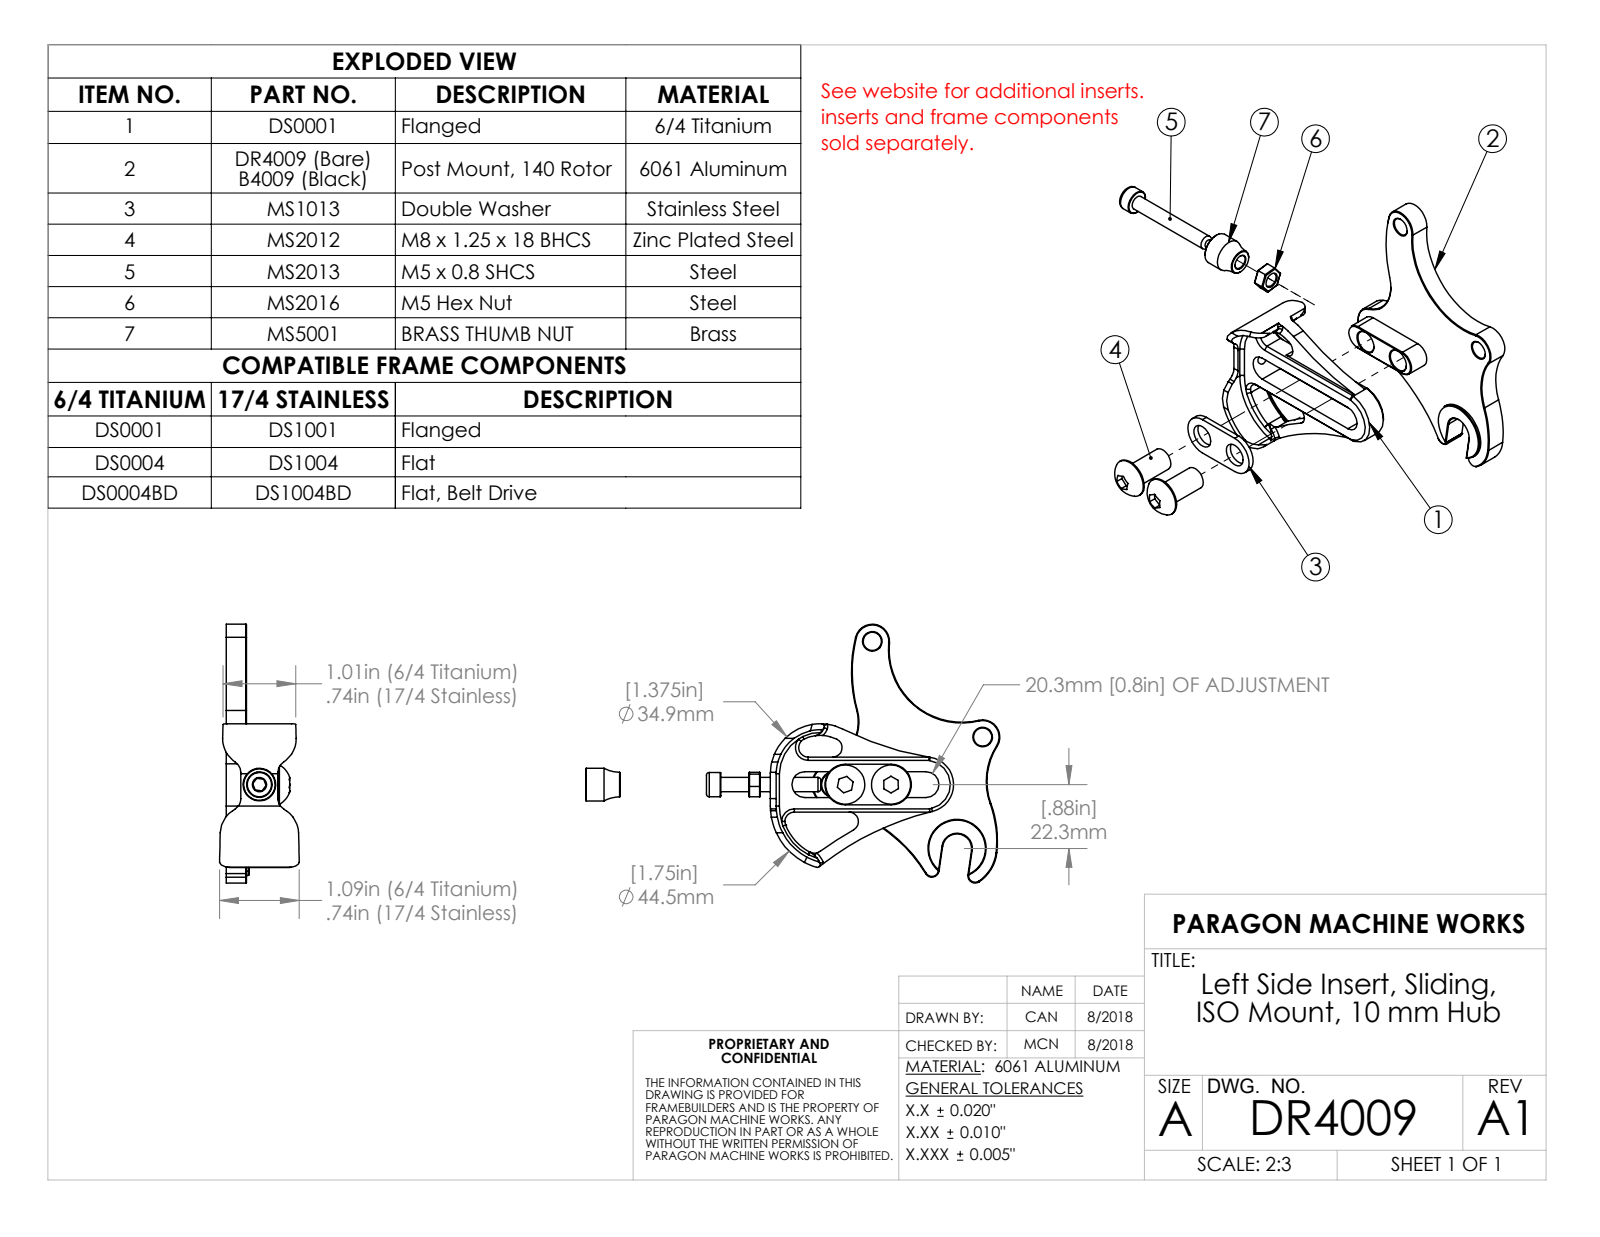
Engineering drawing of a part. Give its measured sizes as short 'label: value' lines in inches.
name: DR4009
written by: SolidWorks 2023 (AUTOMOTIVE_DESIGN)
unit: in
bodies: 1 solid, 73 faces (8 planar, 35 cylindrical, 30 other)
size: 3.53 × 2.37 × 0.585
volume: 1.281 in³; area: 14.18 in²
holes: 2× ⌀0.25, 2× ⌀0.312
bosses: 1× ⌀0.8
rounds: 4× R0.01, 2× R0.1, 2× R0.178, 2× R0.236, 2× R2, 1× R0.2, 1× R0.3, 1× R0.55
face distances: 0.28, 0.356, 0.316, 0.036, 0.585, 0.305, 0.269, 0.4
hole spacings: 0.63, 1.419, 1.985, 2, 2.003, 2.008
